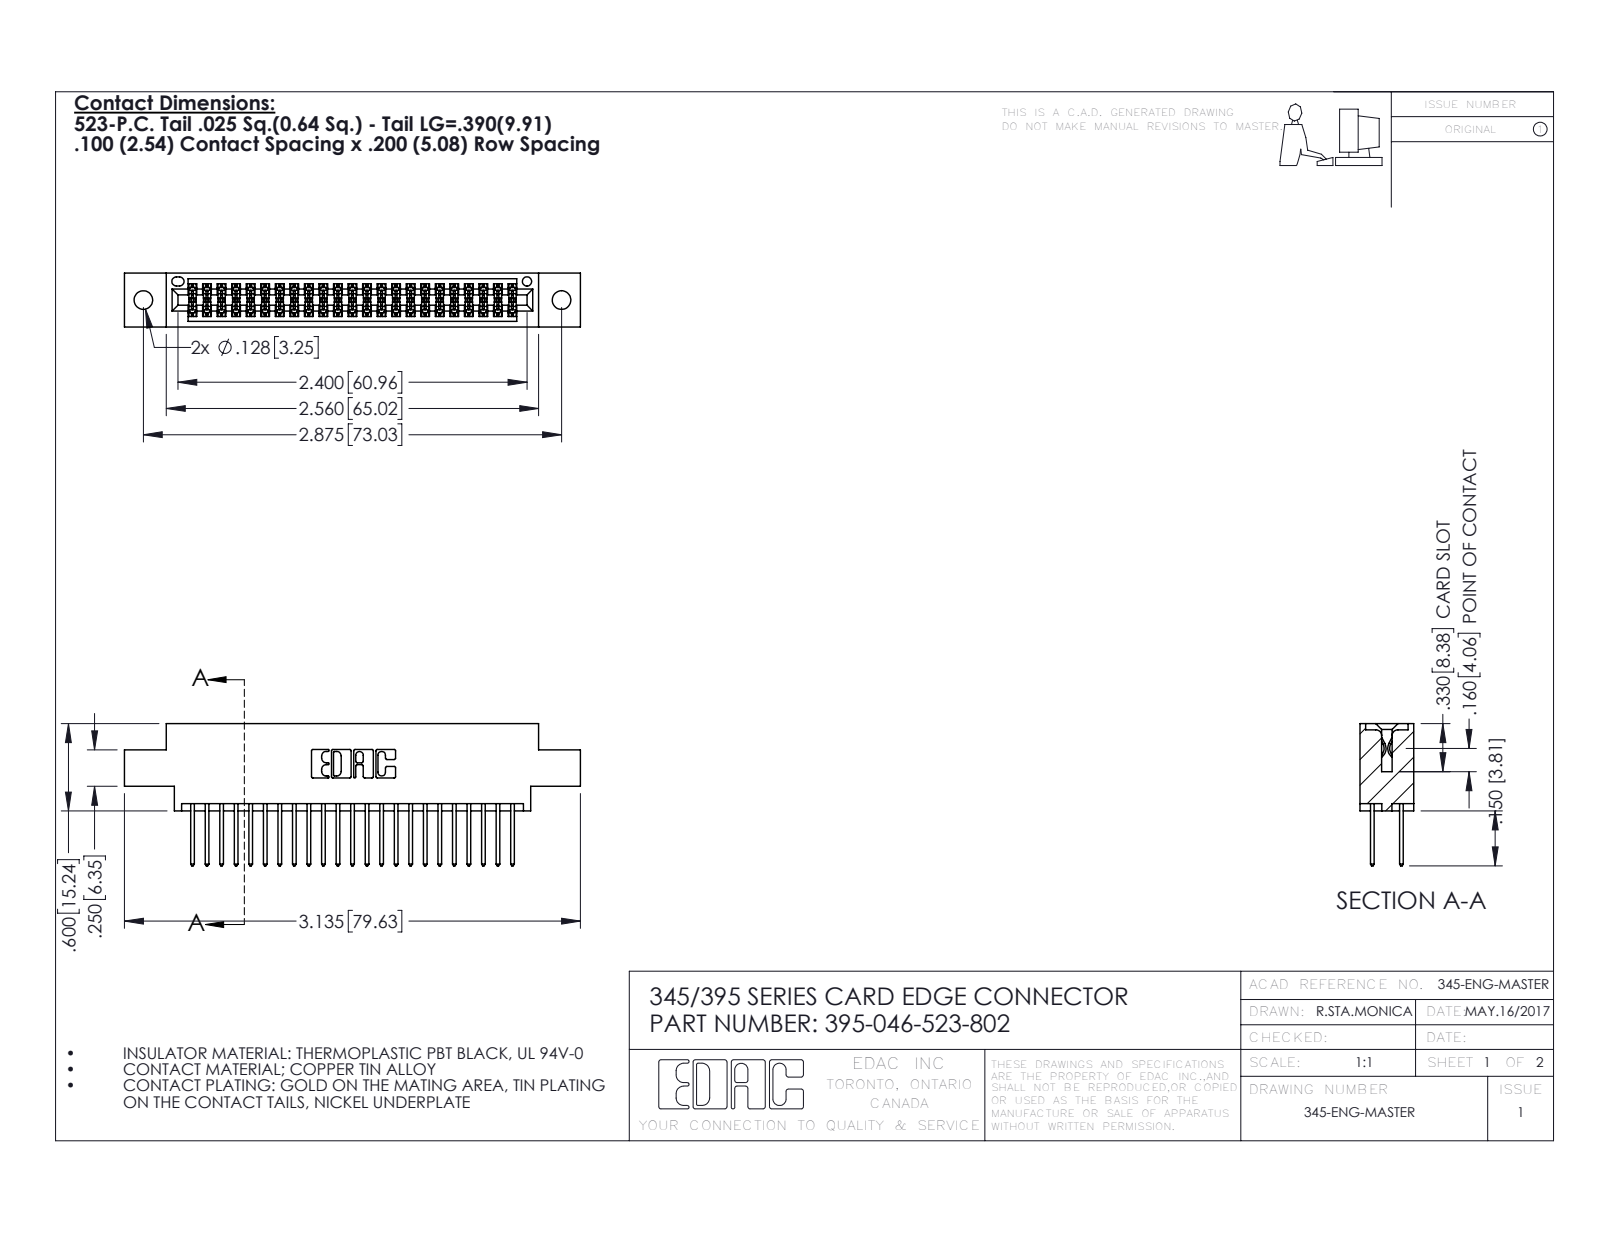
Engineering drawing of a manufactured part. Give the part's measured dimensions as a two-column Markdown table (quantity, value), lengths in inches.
| quantity | value |
| --- | --- |
| part name | 345 Part_0.170 Offset - 0.128 Dia; 395-046-523-802; 345-292-001_345-293-123 |
| STEP written by | SolidWorks 2016 (CONFIG_CONTROL_DESIGN) |
| units | inches |
| bodies | 47 solids, 2430 faces (1602 planar, 828 cylindrical, 0 other) |
| overall size | 3.135 × 0.977 × 0.37 |
| volume | 0.458 in³ |
| surface area | 17.08 in² |
| round holes (diameter × count) | 0.128 × 2, 0.064 × 1 |
| partial cylindrical surfaces (radius × count) | 0.006 × 69, 0.01 × 46, 0.01 × 22, 0.007 × 6, 0.031 × 6, 0.026 × 3, 0.014 × 2, 0.019 × 2 |
| main face-to-face distances | 0.298, 0.072, 0.2, 0.37, 0.098, 0.272, 0.025, 0.225, 0.175, 0.15 |
| hole center spacings | 0.27, 2.641, 2.875 |
